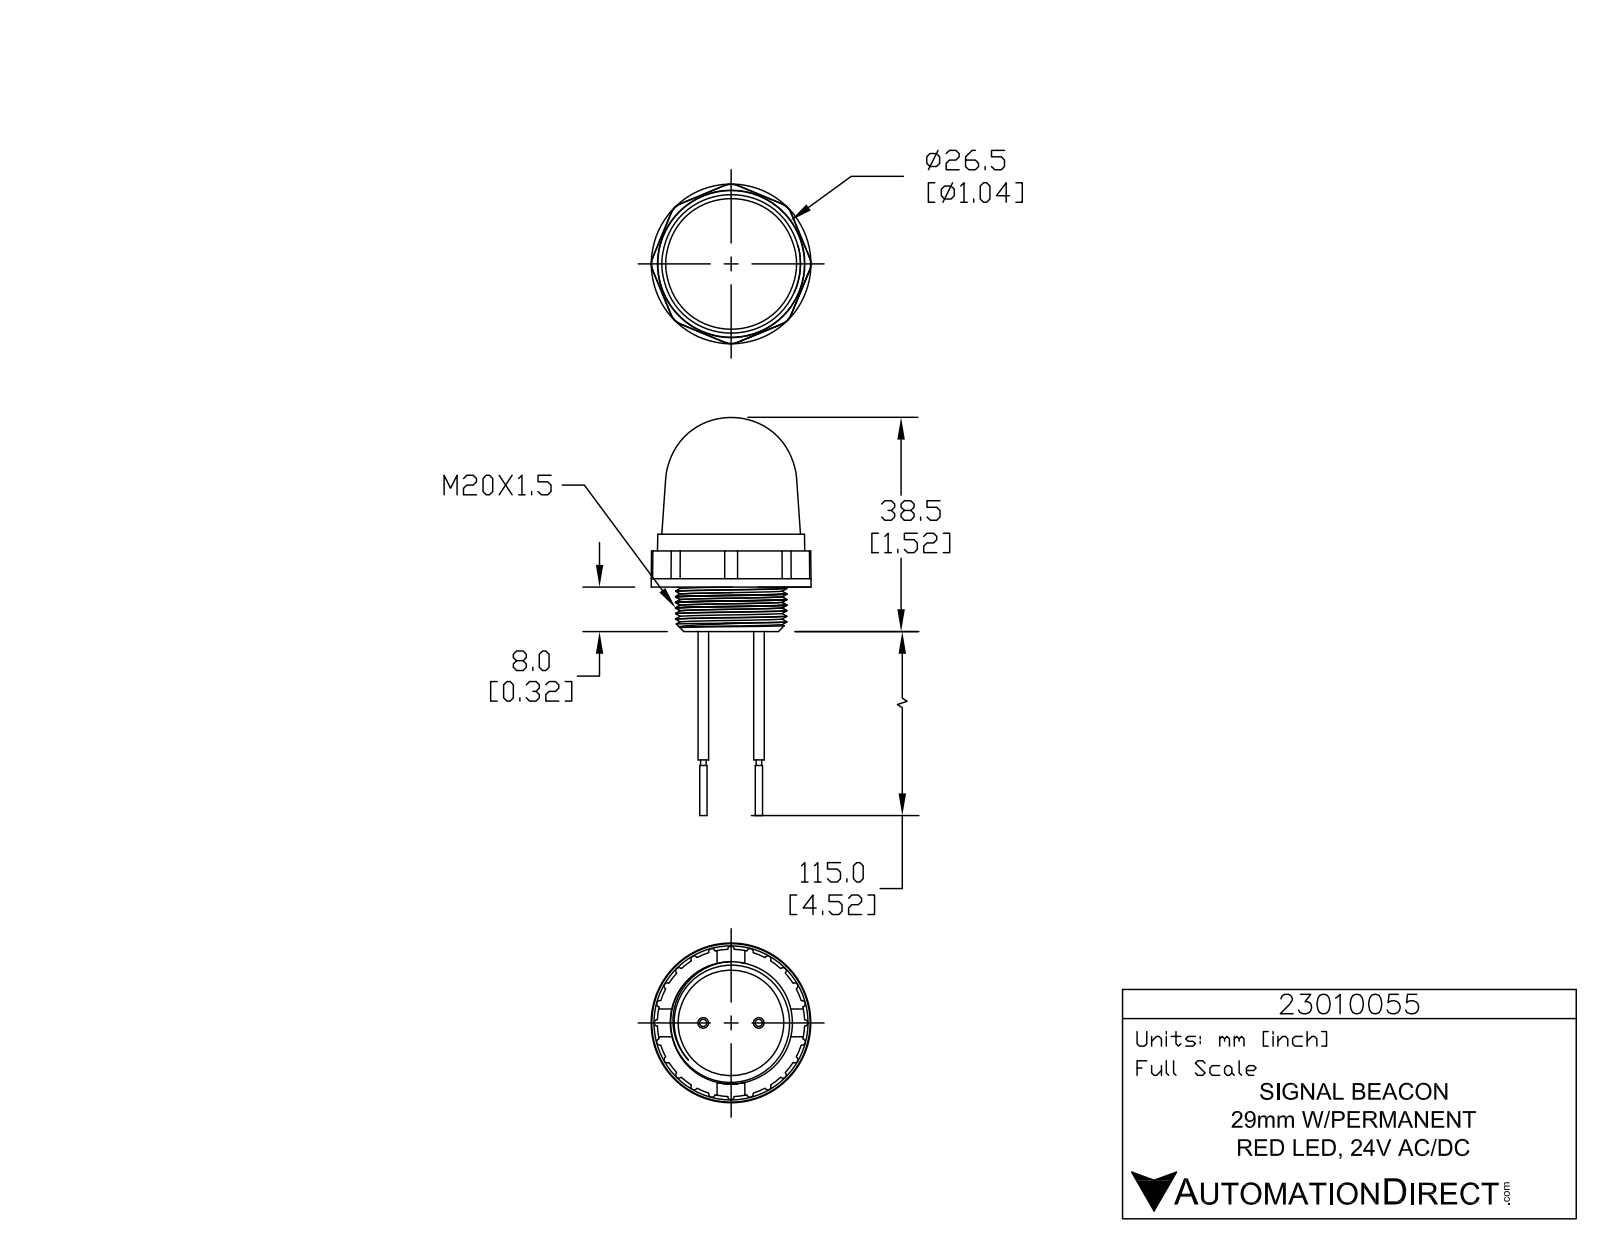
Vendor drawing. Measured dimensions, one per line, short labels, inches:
name: 23010055
written by: SolidWorks 2017 (AUTOMOTIVE_DESIGN)
unit: in
bodies: 1 solid, 844 faces (551 planar, 203 cylindrical, 90 other)
size: 2.82 × 1.131 × 1.131
volume: 0.978 in³; area: 8.158 in²
holes: 3× ⌀0.02, 1× ⌀0.807
bosses: 3× ⌀0.113, 3× ⌀0.028, 2× ⌀0.075, 2× ⌀0.051, 2× ⌀0.039, 1× ⌀1.131, 1× ⌀1.122, 1× ⌀0.894
rounds: 8× R0.118, 6× R0.004, 6× R0.004, 6× R0.004, 6× R0.065, 3× R0.005, 3× R0.007, 3× R0.008
face distances: 0.276, 0.374, 0.039, 0.315, 0.65, 0.638, 0.362, 0.689, 0.413, 0.051
